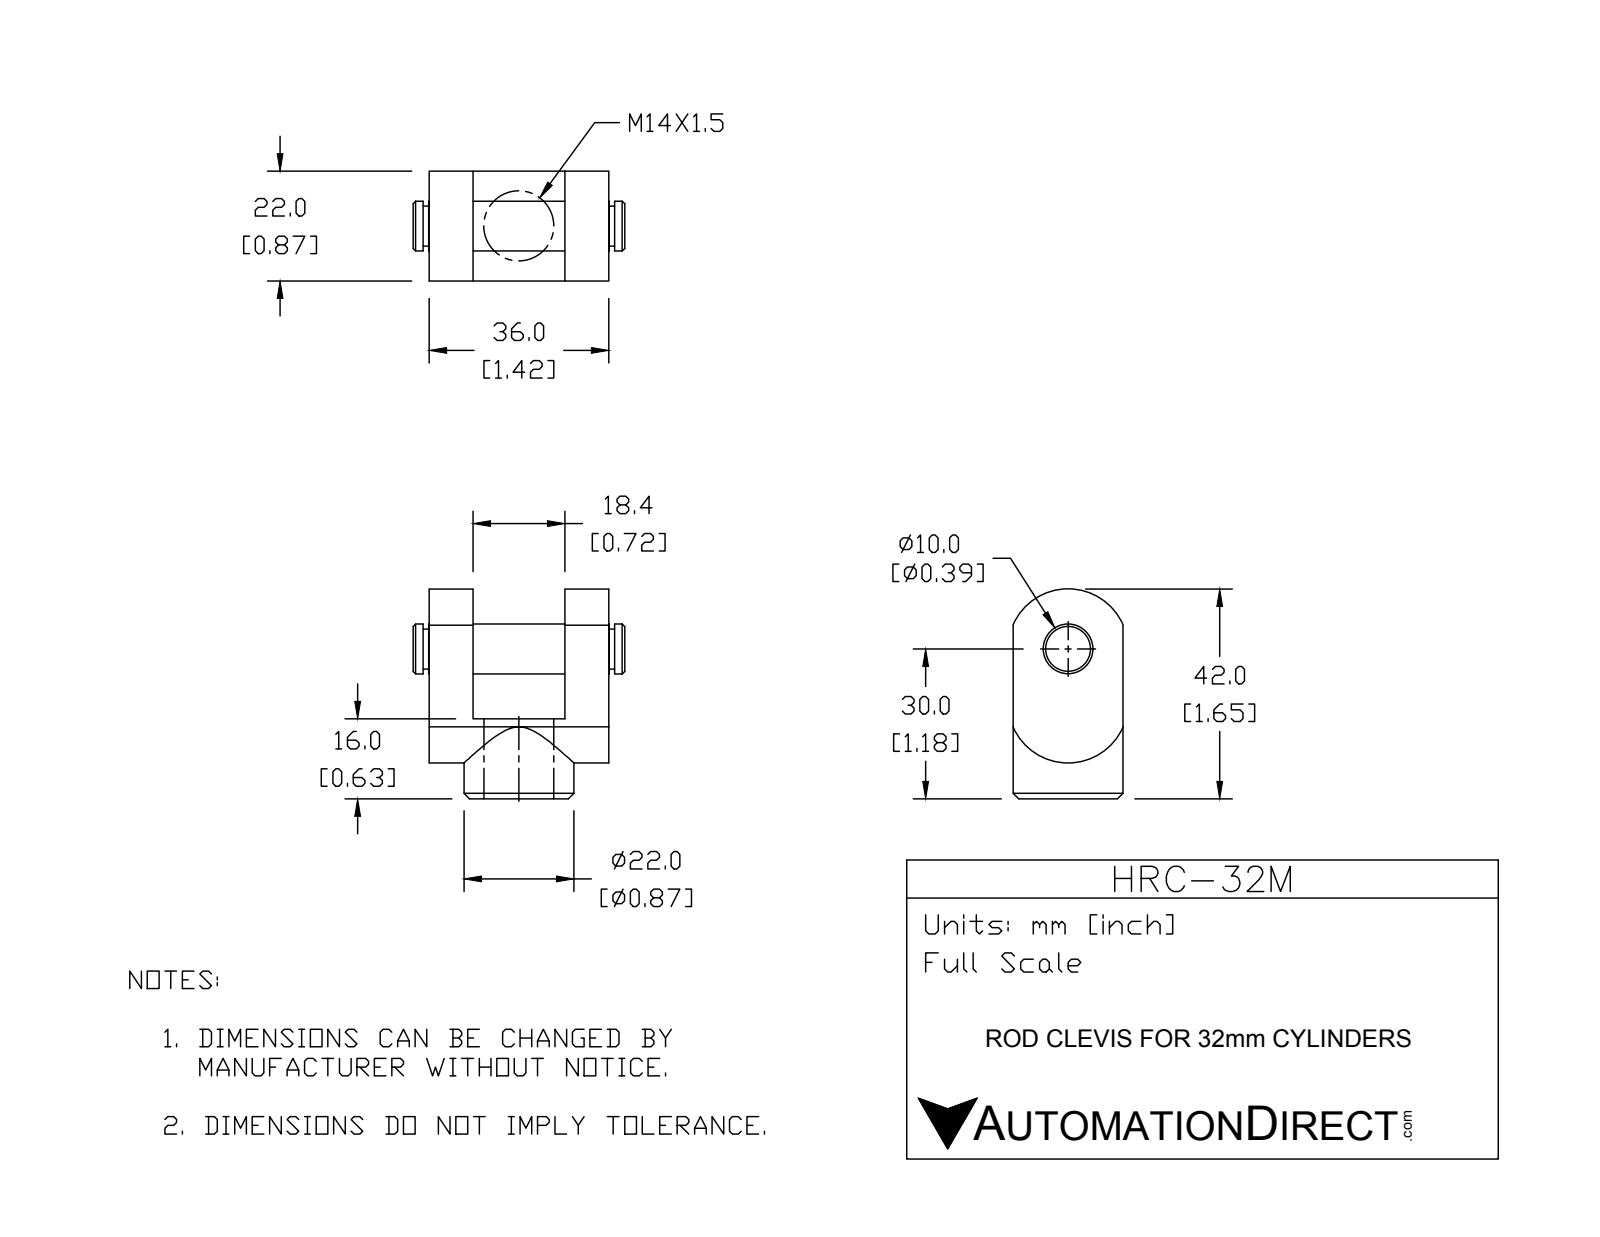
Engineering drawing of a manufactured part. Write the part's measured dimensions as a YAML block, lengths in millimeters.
part_name: "HRC-32M"
step_written_by: "SolidWorks 2015 (CONFIG_CONTROL_DESIGN)"
units: millimeters
bodies: {solids: 2, faces: 46, planar: 14, cylindrical: 22, other: 10}
overall_size: [42.4, 42, 22]
volume: 17803
surface_area: 7848
round_holes:
  - {diameter: 12.5, count: 1}
round_bosses_or_shafts:
  - {diameter: 22, count: 1}
  - {diameter: 10, count: 1}
  - {diameter: 8, count: 1}
partial_cylinders:
  - {radius: 12, count: 2}
face_to_face_distances: [8.8, 27.2, 36, 18.4, 22, 16, 3.2, 12, 30.4, 39.2]
